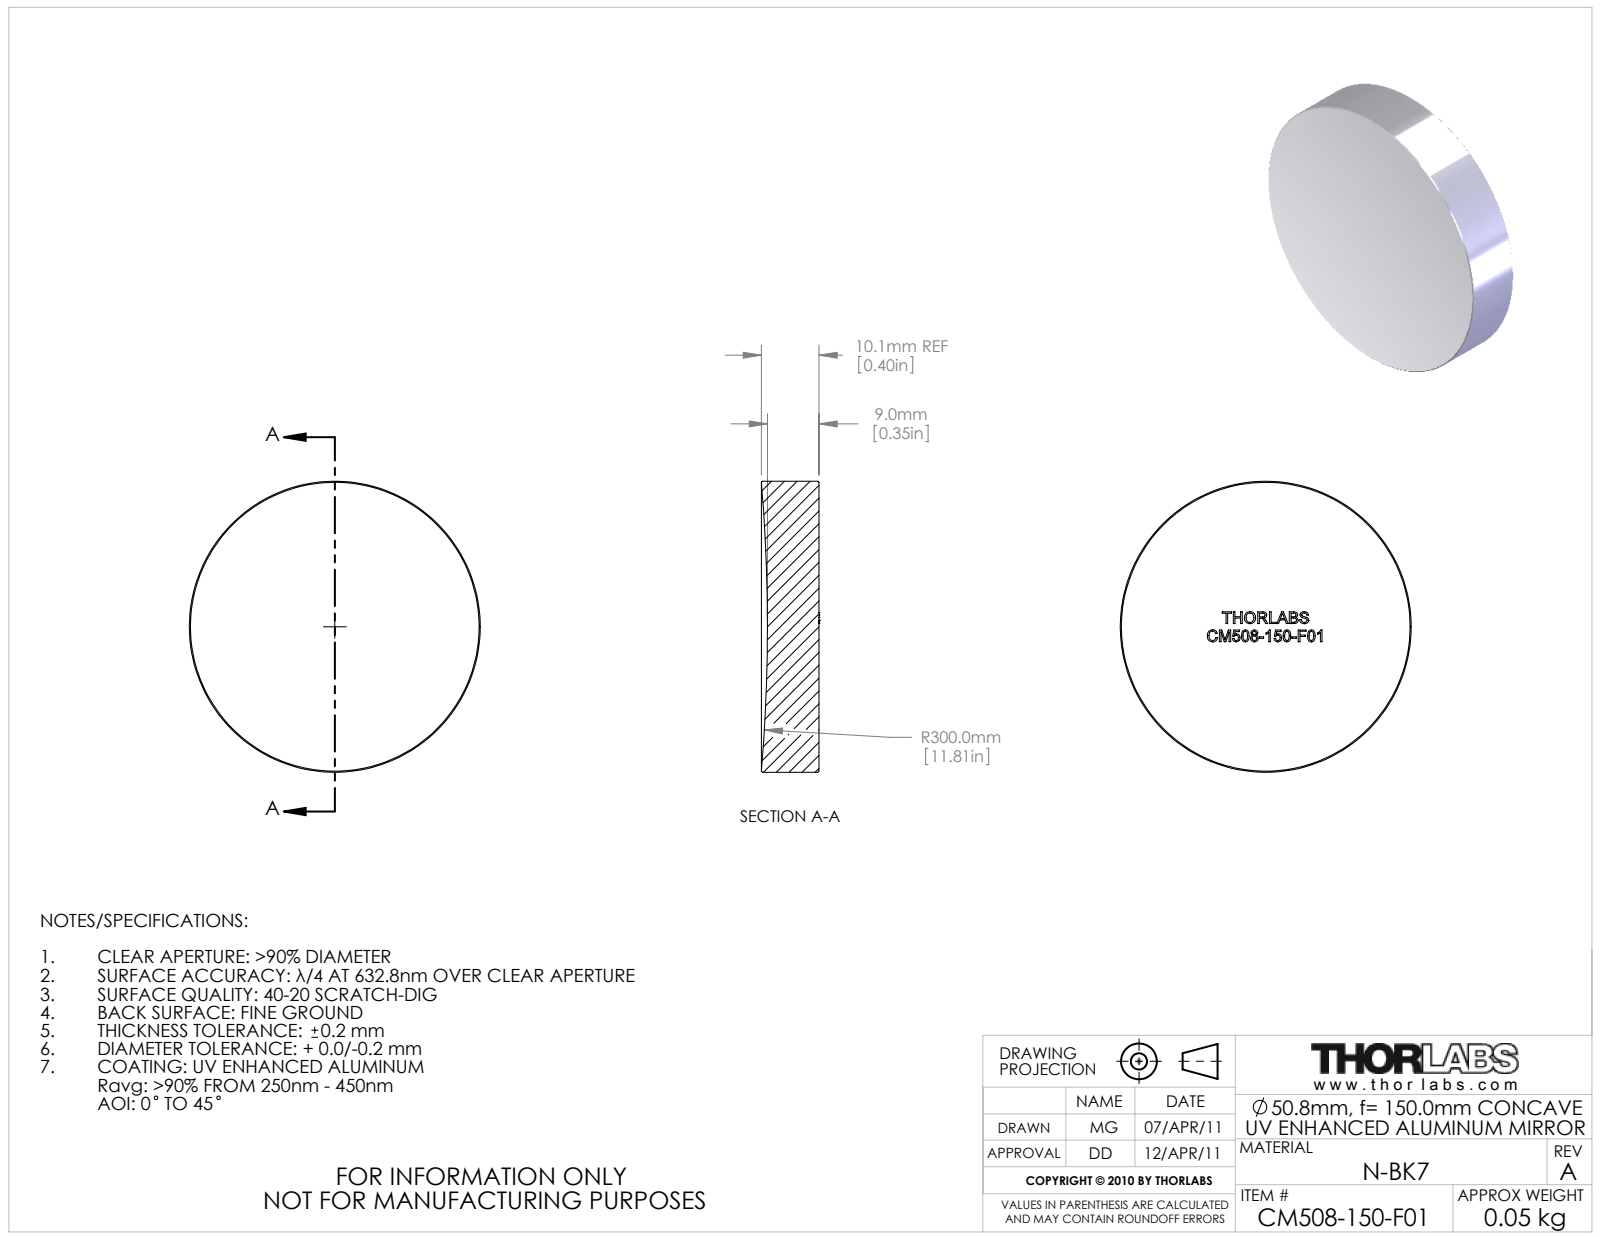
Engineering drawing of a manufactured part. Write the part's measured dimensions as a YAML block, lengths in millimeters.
part_name: "22200-E0W"
step_written_by: "SolidWorks 2011 (AUTOMOTIVE_DESIGN)"
units: millimeters
bodies: {solids: 1, faces: 276, planar: 148, cylindrical: 2, other: 126}
overall_size: [50.8, 50.8, 10.1]
volume: 19320
surface_area: 5626
round_bosses_or_shafts:
  - {diameter: 50.8, count: 1}
face_to_face_distances: [1.2, 3.1, 2.1, 5.5, 8.7, 0.7, 2.5, 1.6, 2.1, 0.5]
